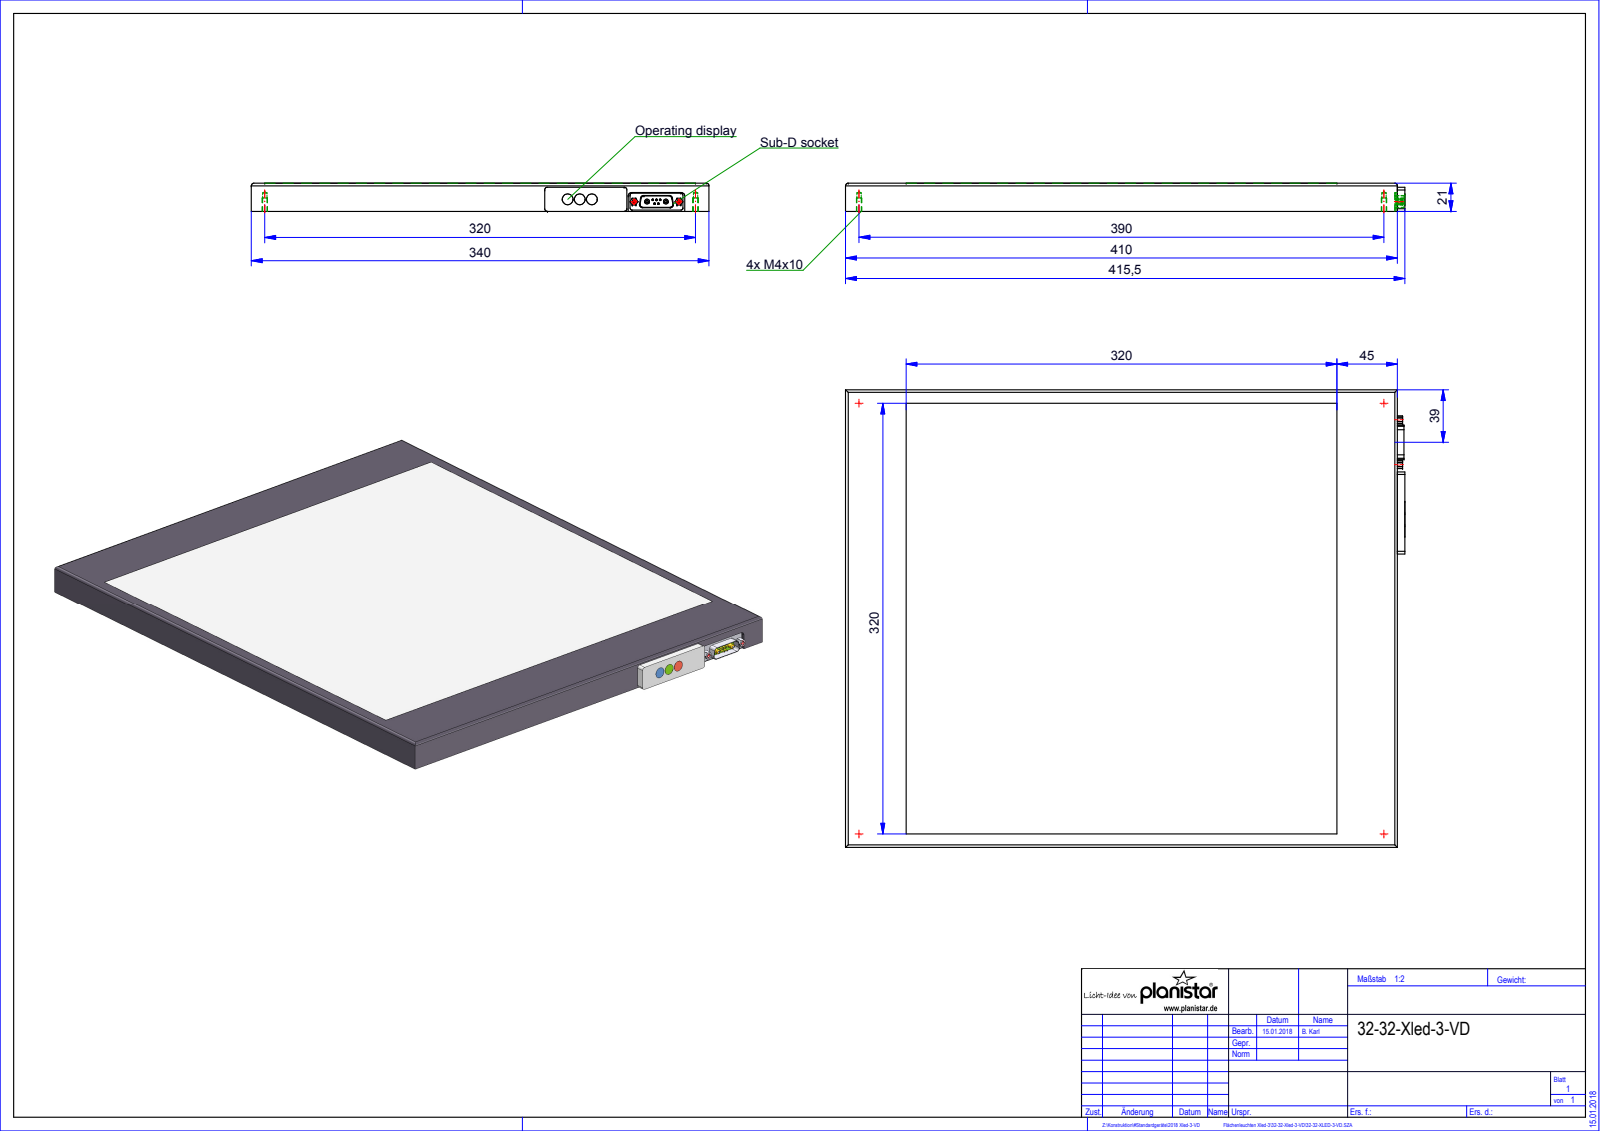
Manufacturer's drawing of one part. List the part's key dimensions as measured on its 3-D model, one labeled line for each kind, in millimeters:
Part name (STEP PRODUCT): Root; Baugruppe_Xled-2-VD; QUADER_0; Baugruppe_Baugruppe (+5 more)
STEP written by: HiCAD 2015 2002.1 Build 408 (AUTOMOTIVE_DESIGN)
Units: millimetres
Bodies: 12 solids, 145 faces (76 planar, 56 cylindrical, 13 other)
Overall size (bounding box): 415.55 × 340 × 21.1
Volume: 2 941 000 mm³ · Surface area: 315 263 mm²
Round holes (diameter × count): ⌀3.3 ×4, ⌀4 ×4, ⌀2.5 ×2, ⌀3 ×2
Round bosses / shafts (diameter × count): ⌀1 ×5, ⌀8 ×3, ⌀3.6 ×2
Partial cylindrical surfaces — rounded edges, fillets, slot ends (radius × count): R0.2 ×12, R2 ×8, R2.5 ×6, R1.5 ×4, R2.1 ×4
Main face-to-face distances: 21.1, 21, 340, 410, 1, 408, 2, 7.5, 415.5, 5.5
Hole centre spacings: 320, 390, 504.48, 33.32
